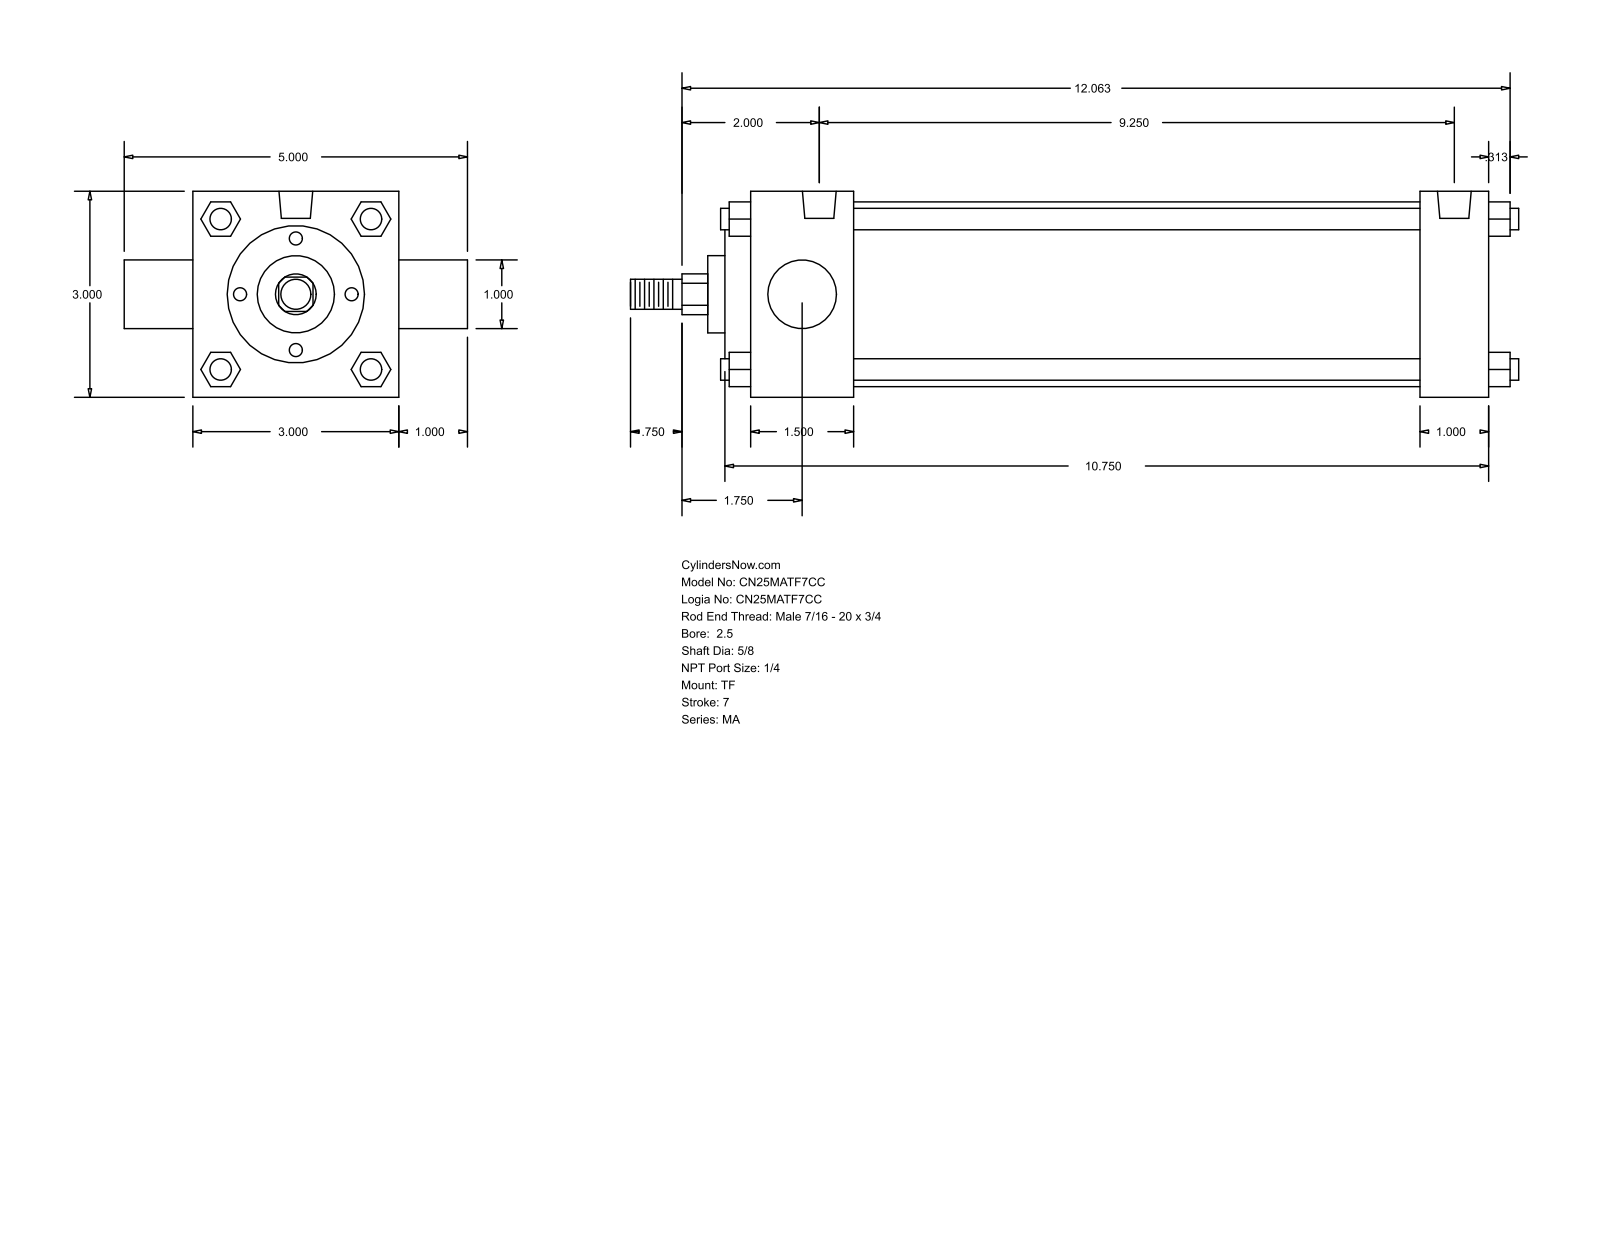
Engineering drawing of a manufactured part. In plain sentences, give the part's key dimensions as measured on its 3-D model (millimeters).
The part is named "MA_TF__0250_0.625". Its 3-D file was written by "GSSL Pune (CONFIG_CONTROL_DESIGN)". It is 0 solids with 122 faces: 93 planar, 29 cylindrical and 0 other. Overall it measures 328.61 by 127 by 76.2 millimeters. Round holes: 3 of diameter 7.94, 2 of diameter 12.49. Round bosses or shafts: 4 of diameter 7.94, 1 of diameter 68.33, 1 of diameter 50.8, 1 of diameter 28.57, 1 of diameter 25.4, 1 of diameter 15.88, 1 of diameter 11.11. Partial cylindrical surfaces (rounded edges, fillets, slot ends): 1 of radius 7.54. The main face-to-face distances are 76.2, 273.05, 25.4, 38.1, 247.65, 209.55, 234.95, 12.7, 9.52, 47.62. The hole center spacings are 234.95.
